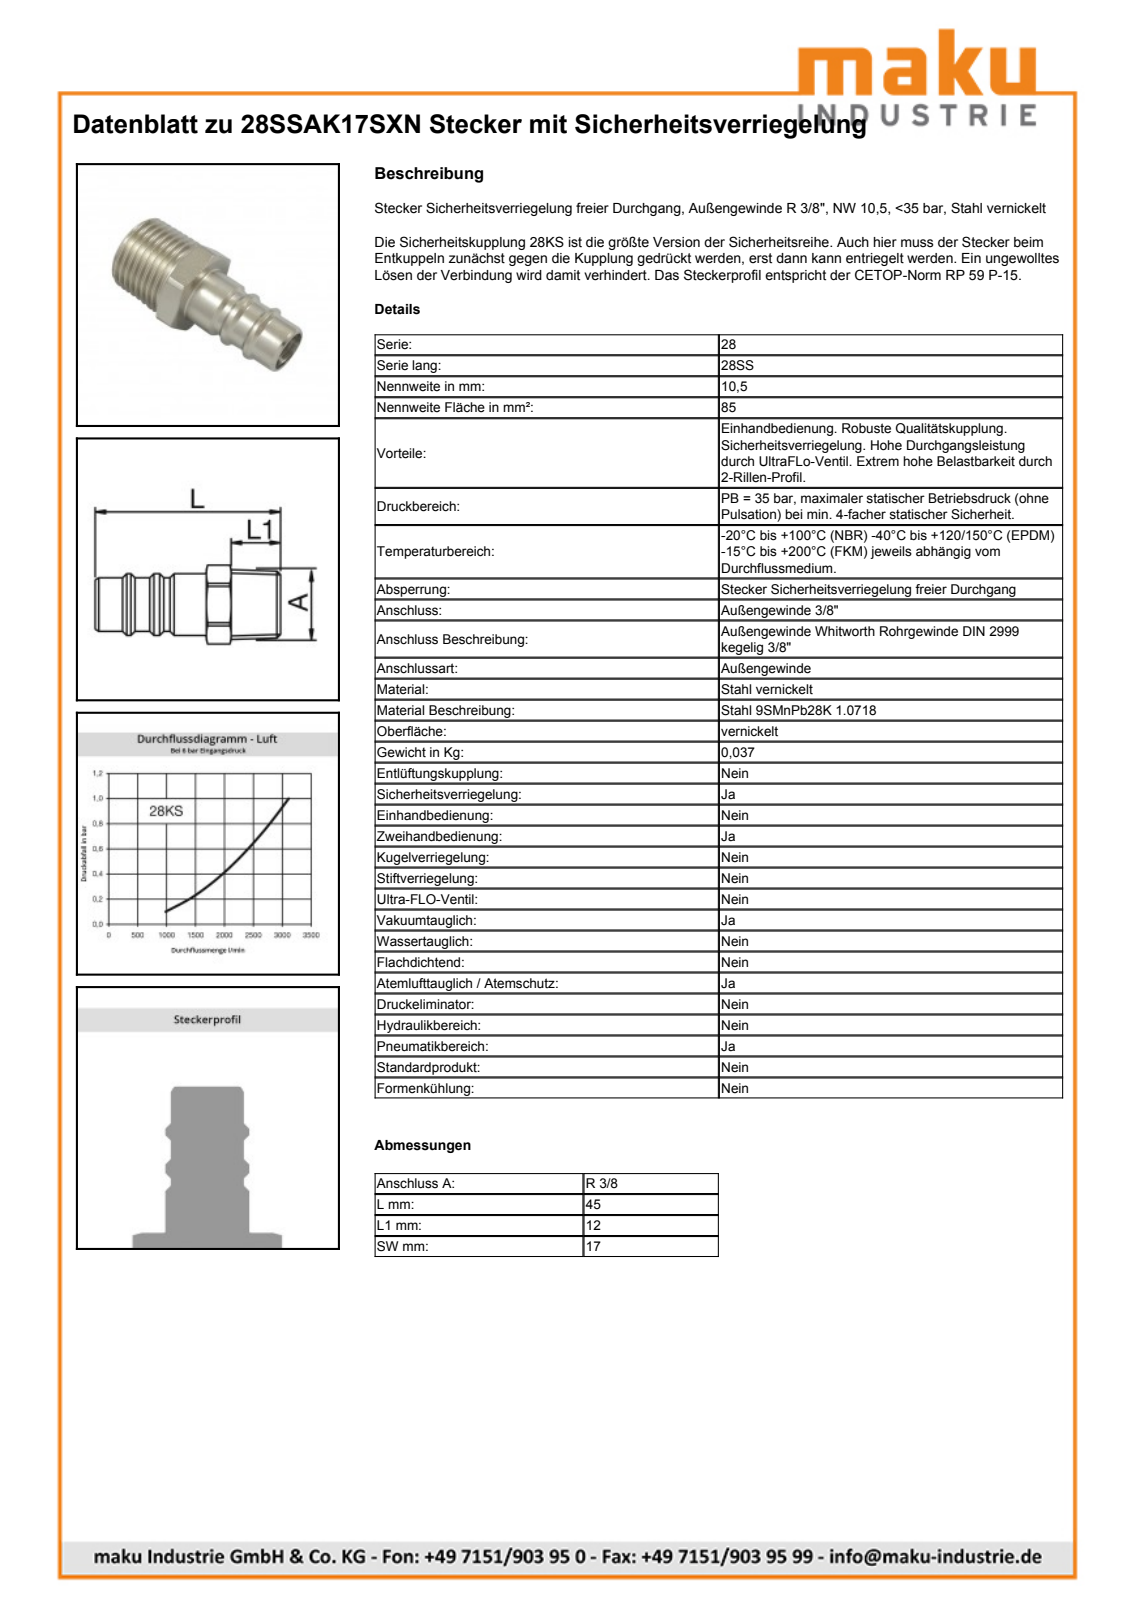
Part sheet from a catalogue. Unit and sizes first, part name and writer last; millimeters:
Units: millimetres
Overall size (bounding box): 45 × 19.15 × 17
Round holes (diameter × count): ⌀10.5 ×1
Round bosses / shafts (diameter × count): ⌀15 ×1, ⌀13 ×1
Partial cylindrical surfaces — rounded edges, fillets, slot ends (radius × count): R9.57 ×1
Main face-to-face distances: 17, 18, 27, 45
Volume: 4 322 mm³ · Surface area: 3 931 mm²
Bodies: 1 solid, 44 faces (9 planar, 13 cylindrical, 22 other)
Part name (STEP PRODUCT): D103258
STEP written by: Autodesk Inventor 2011 (AUTOMOTIVE_DESIGN)
